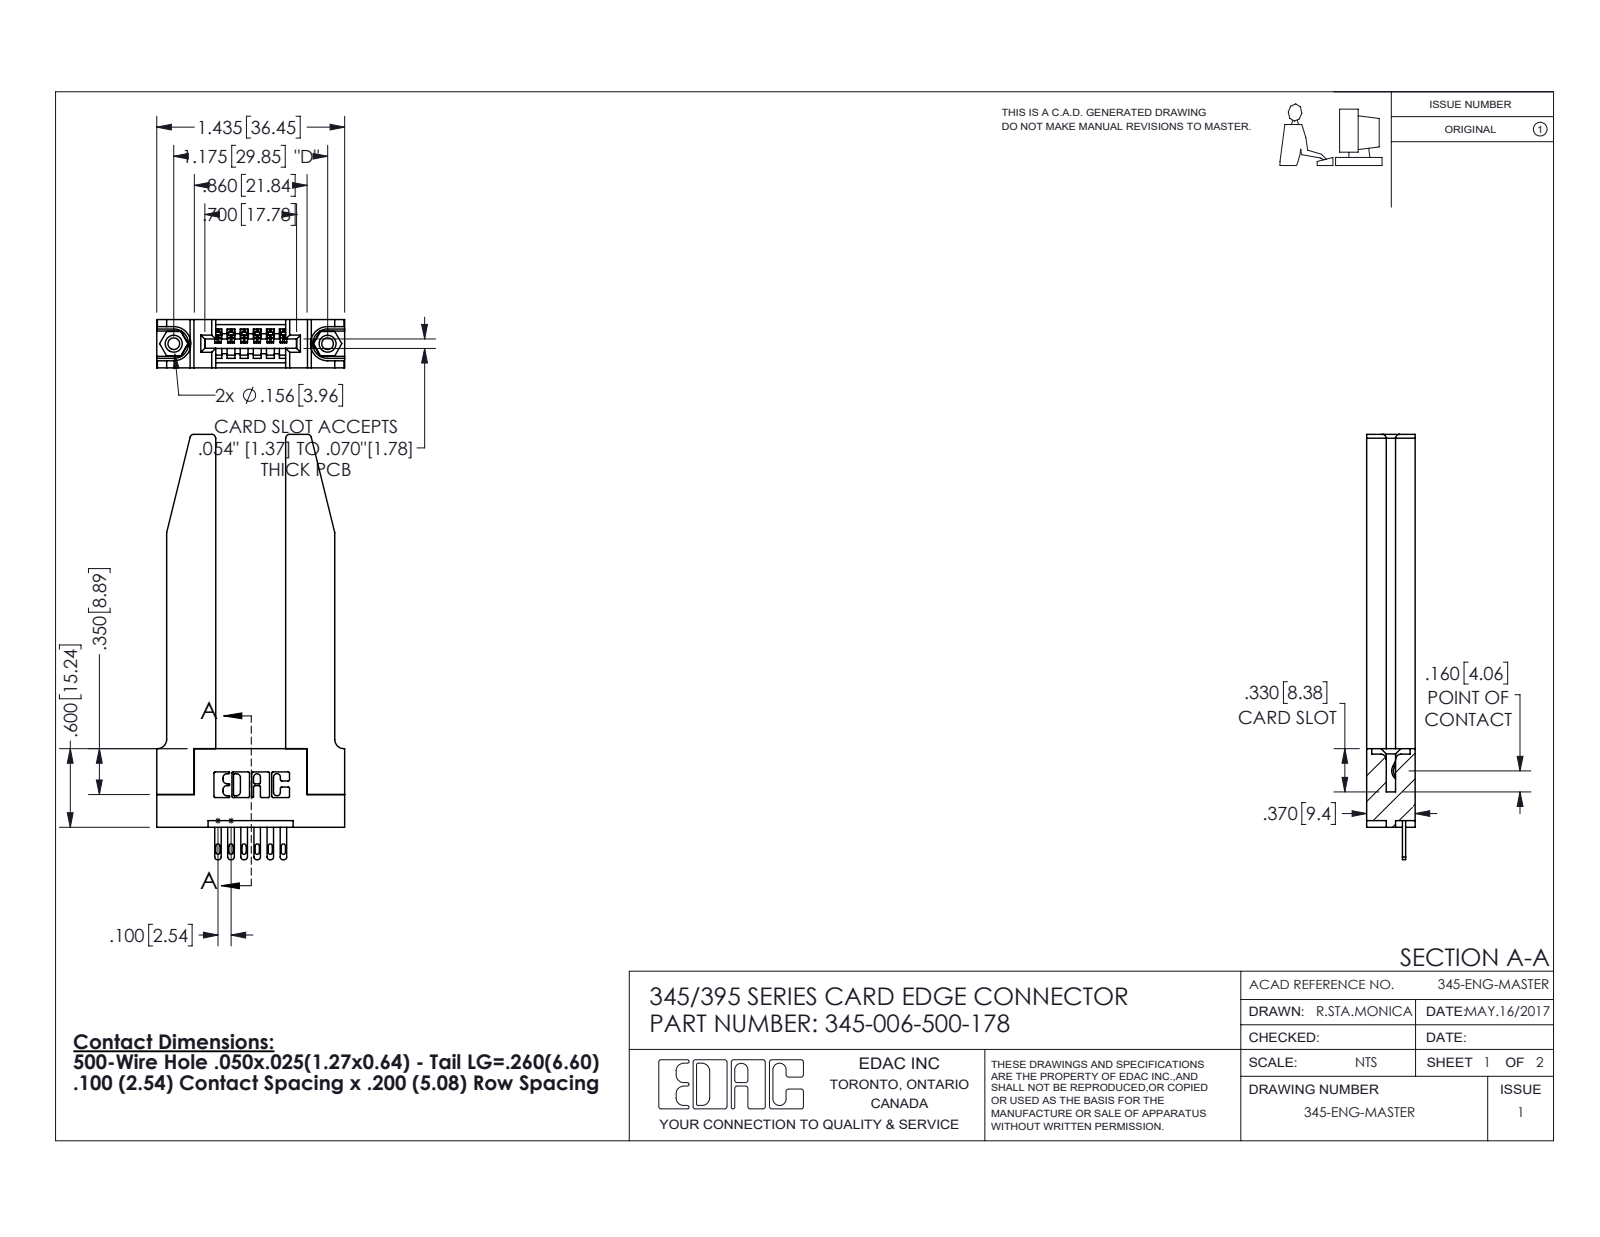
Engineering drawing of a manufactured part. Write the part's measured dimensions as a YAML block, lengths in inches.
part_name: "345-006-500-178; 345-220-078_345-220-078; 345-250-001_345-250-001-102; 345-292-001_345-293-100 (+1 more)"
step_written_by: "SolidWorks 2016 (CONFIG_CONTROL_DESIGN)"
units: inches
bodies: {solids: 11, faces: 684, planar: 426, cylindrical: 206, other: 52}
overall_size: [3.247, 1.436, 0.37]
volume: 0.668
surface_area: 16.41
round_holes:
  - {diameter: 0.089, count: 2}
  - {diameter: 0.125, count: 2}
  - {diameter: 0.156, count: 2}
  - {diameter: 0.064, count: 1}
round_bosses_or_shafts:
  - {diameter: 0.155, count: 2}
partial_cylinders:
  - {radius: 0.01, count: 22}
  - {radius: 0.006, count: 12}
  - {radius: 0.016, count: 12}
  - {radius: 0.02, count: 12}
  - {radius: 0.03, count: 8}
  - {radius: 0.007, count: 6}
  - {radius: 0.031, count: 6}
  - {radius: 0.026, count: 3}
face_to_face_distances: [0.37, 0.15, 0.22, 0.535, 0.072, 0.148, 0.298, 0.077, 0.2, 0.095]
hole_center_spacings: [0.27, 0.946, 1.175]
